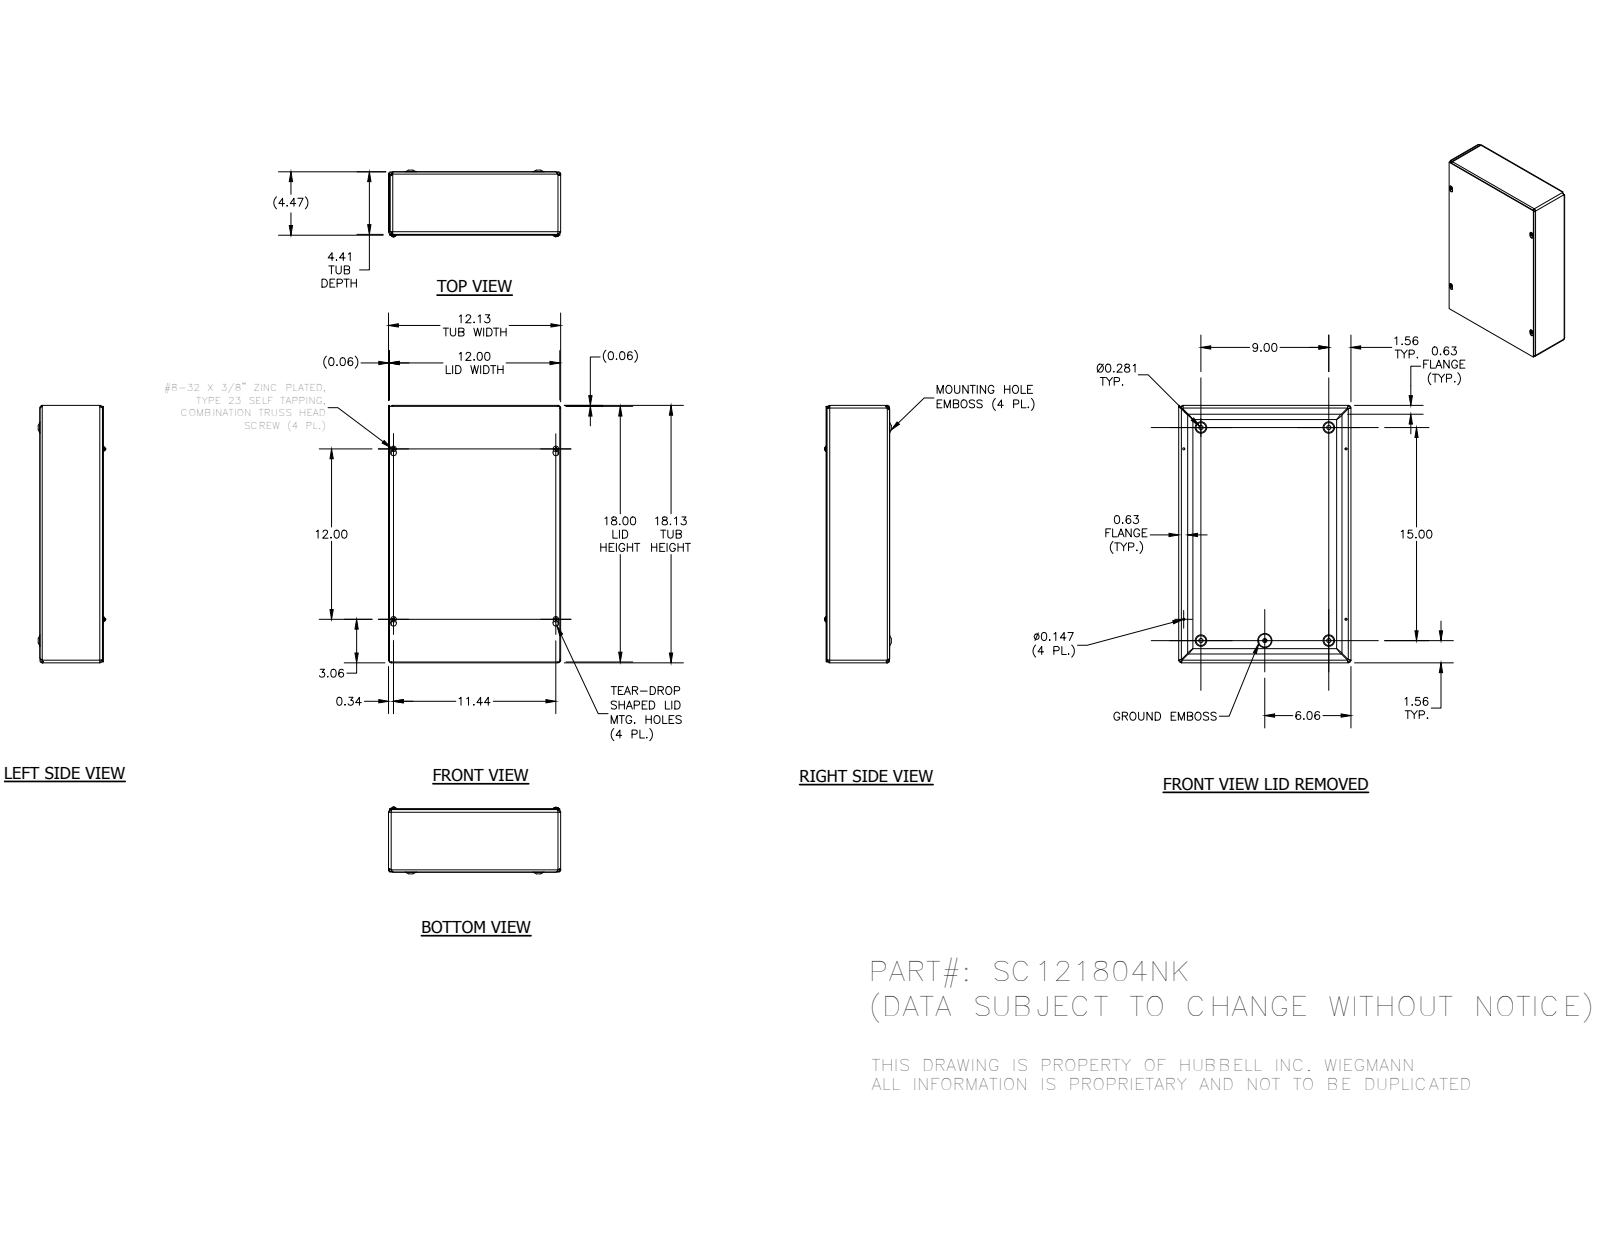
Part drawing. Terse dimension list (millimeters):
name: SC1218BKP; SC121804NKWRA; SC1218LID; 34056 (+1 more)
written by: Autodesk Inventor 2014 (AUTOMOTIVE_DESIGN)
unit: mm
bodies: 7 solids, 357 faces (132 planar, 67 cylindrical, 158 other)
size: 460.38 × 307.98 × 119.2
volume: 779 977 mm³; area: 999 683 mm²
holes: 4× ⌀3.73, 4× ⌀7.62, 1× ⌀4.19
bosses: 4× ⌀9.75, 4× ⌀4.17, 1× ⌀5.8
rounds: 12× R3.17, 8× R4.75, 4× R1.4, 4× R1.57, 4× R2.38, 4× R2.97, 4× R3.15, 4× R3.96
face distances: 1.57, 110.32, 111.89, 1.59, 111.91, 113.48, 1.58, 458.8, 306.4, 304.83
hole spacings: 49.09, 344.29, 114.3, 228.6, 262.33, 262.34, 290.51, 304.8
